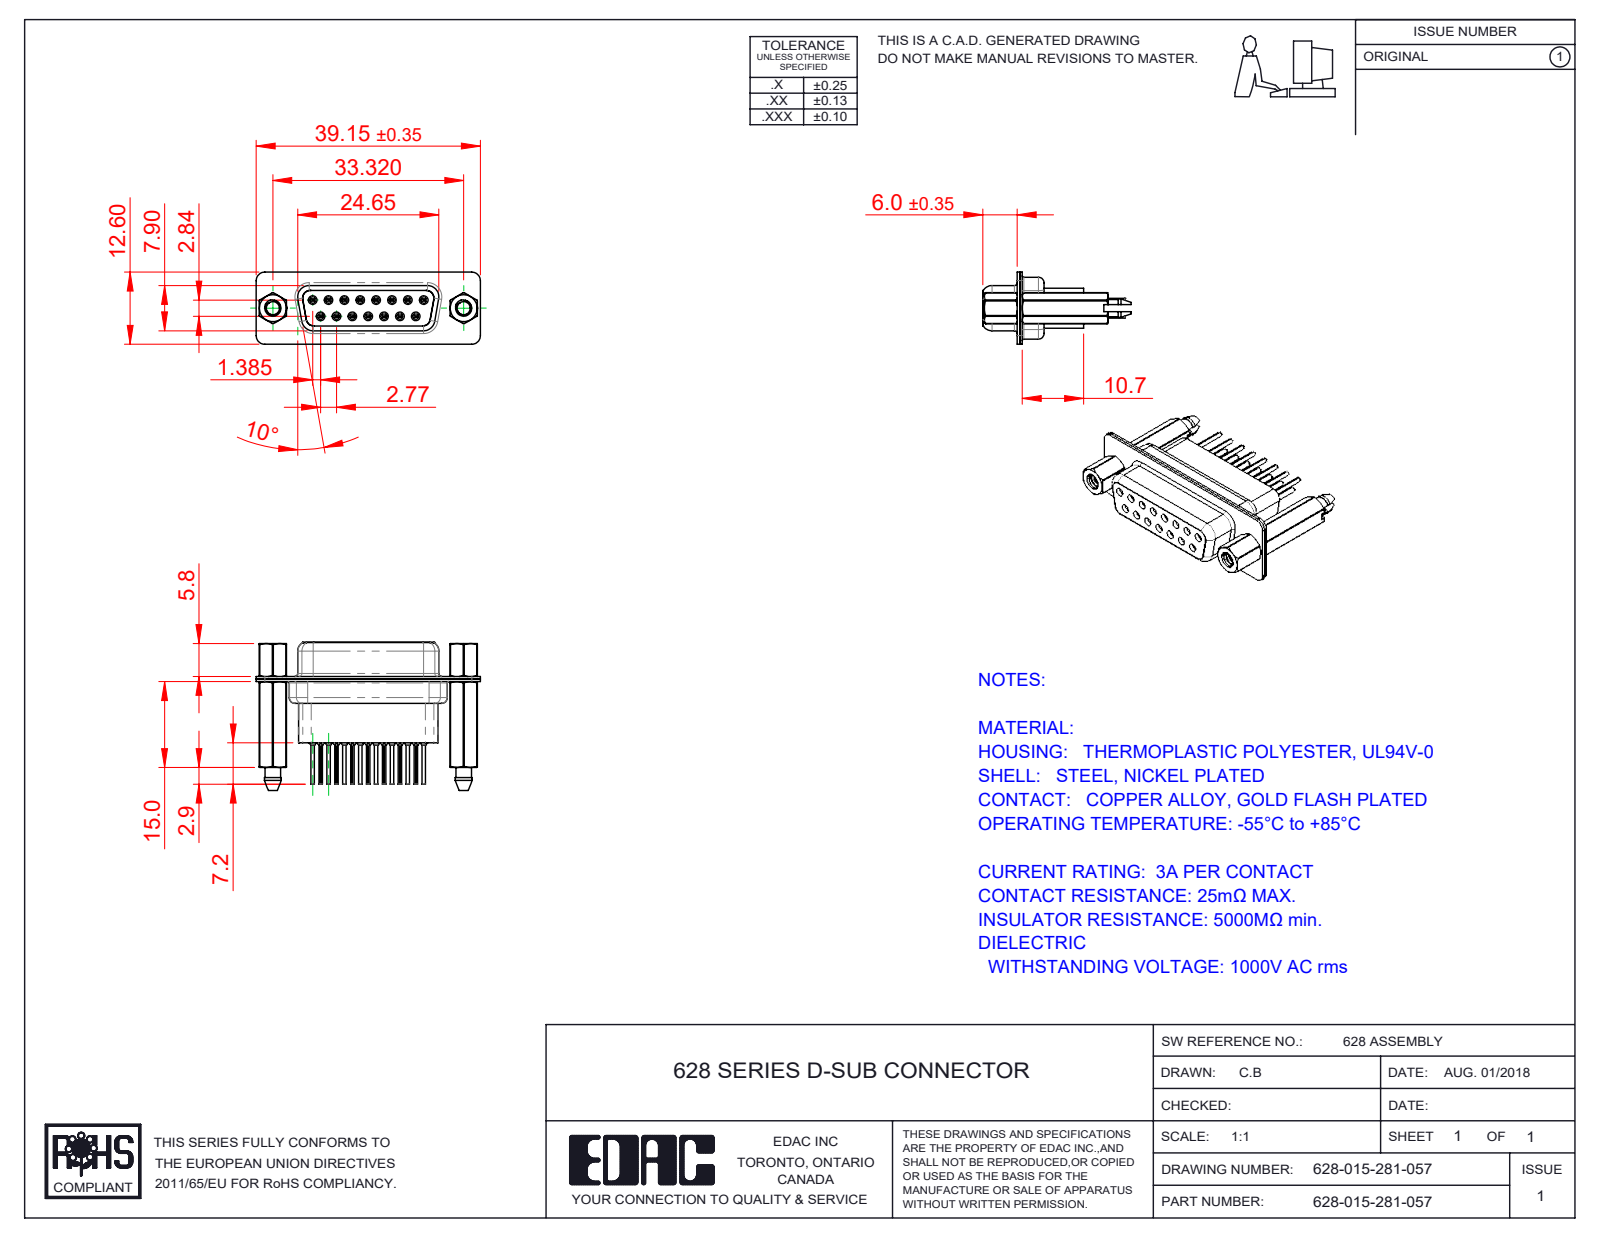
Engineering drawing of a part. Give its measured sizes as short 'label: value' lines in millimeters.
name: 628 4-40 Threaded Boardlock_HP81; 628 Housing_15 HP; 628 Contact Row 1_71; 628-015-281-057 (+4 more)
written by: SolidWorks 2020 (CONFIG_CONTROL_DESIGN)
unit: mm
bodies: 22 solids, 2324 faces (586 planar, 736 cylindrical, 1002 other)
size: 39.15 × 25.9 × 12.6
volume: 3 892 mm³; area: 8 967 mm²
holes: 15× ⌀0.2, 15× ⌀0.8, 15× ⌀0.9, 15× ⌀1.1, 15× ⌀1.6, 8× ⌀1.7, 2× ⌀2.26, 2× ⌀2.29, 2× ⌀4, 2× ⌀4.05, 2× ⌀4.85
bosses: 15× ⌀2, 15× ⌀1.5, 15× ⌀1.2, 15× ⌀0.6, 2× ⌀4.95, 2× ⌀4.8, 2× ⌀2.79
rounds: 30× R0.1, 20× R1.5, 15× R0.28, 12× R2, 8× R1.35, 6× R1.6, 4× R0.25, 4× R0.5
face distances: 0.45, 0.4, 4.76, 0.9, 6.6, 8.5, 1.9, 7, 16.66, 1.4
hole spacings: 3.16, 2.77, 5.54, 8.31, 11.08, 5.03, 5.04, 7.48
